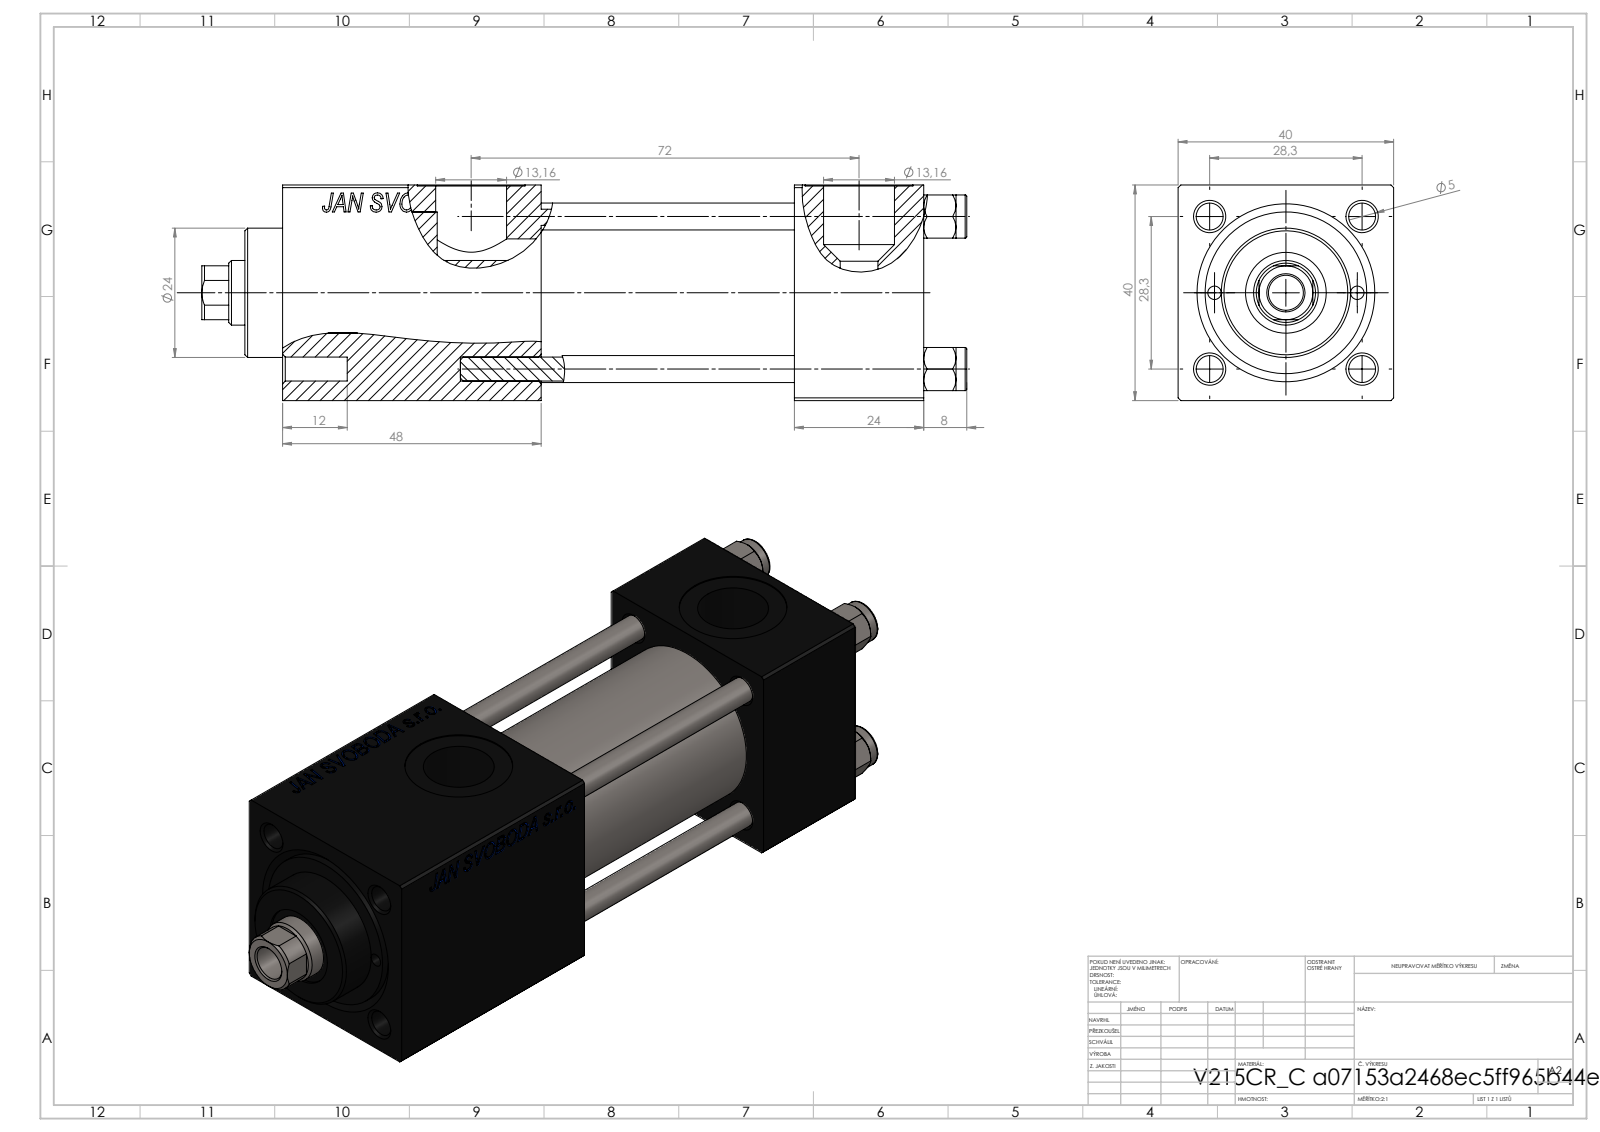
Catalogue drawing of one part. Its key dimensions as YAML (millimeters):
part_name: "V215CR_VCP_C; V215CR_C_Body; V215CR_C_TYCINKA; NUT_M5_C (+1 more)"
step_written_by: "SolidWorks 2019 (CONFIG_CONTROL_DESIGN)"
units: millimeters
bodies: {solids: 11, faces: 1154, planar: 527, cylindrical: 91, other: 536}
overall_size: [142, 40, 40]
volume: 142260
surface_area: 54521
round_holes:
  - {diameter: 5, count: 4}
  - {diameter: 20, count: 3}
  - {diameter: 2.5, count: 2}
  - {diameter: 7, count: 2}
  - {diameter: 13.16, count: 2}
  - {diameter: 6.5, count: 1}
  - {diameter: 12, count: 1}
  - {diameter: 15, count: 1}
  - {diameter: 25, count: 1}
  - {diameter: 30, count: 1}
round_bosses_or_shafts:
  - {diameter: 8, count: 4}
  - {diameter: 31, count: 1}
  - {diameter: 24, count: 1}
partial_cylinders:
  - {radius: 5.5, count: 1}
face_to_face_distances: [40, 24, 90.3, 66.3, 48, 71, 47, 19.3, 119, 95]
hole_center_spacings: [14.18, 20.01, 28.3, 30.84, 13.25, 40.02, 26.5, 72]
